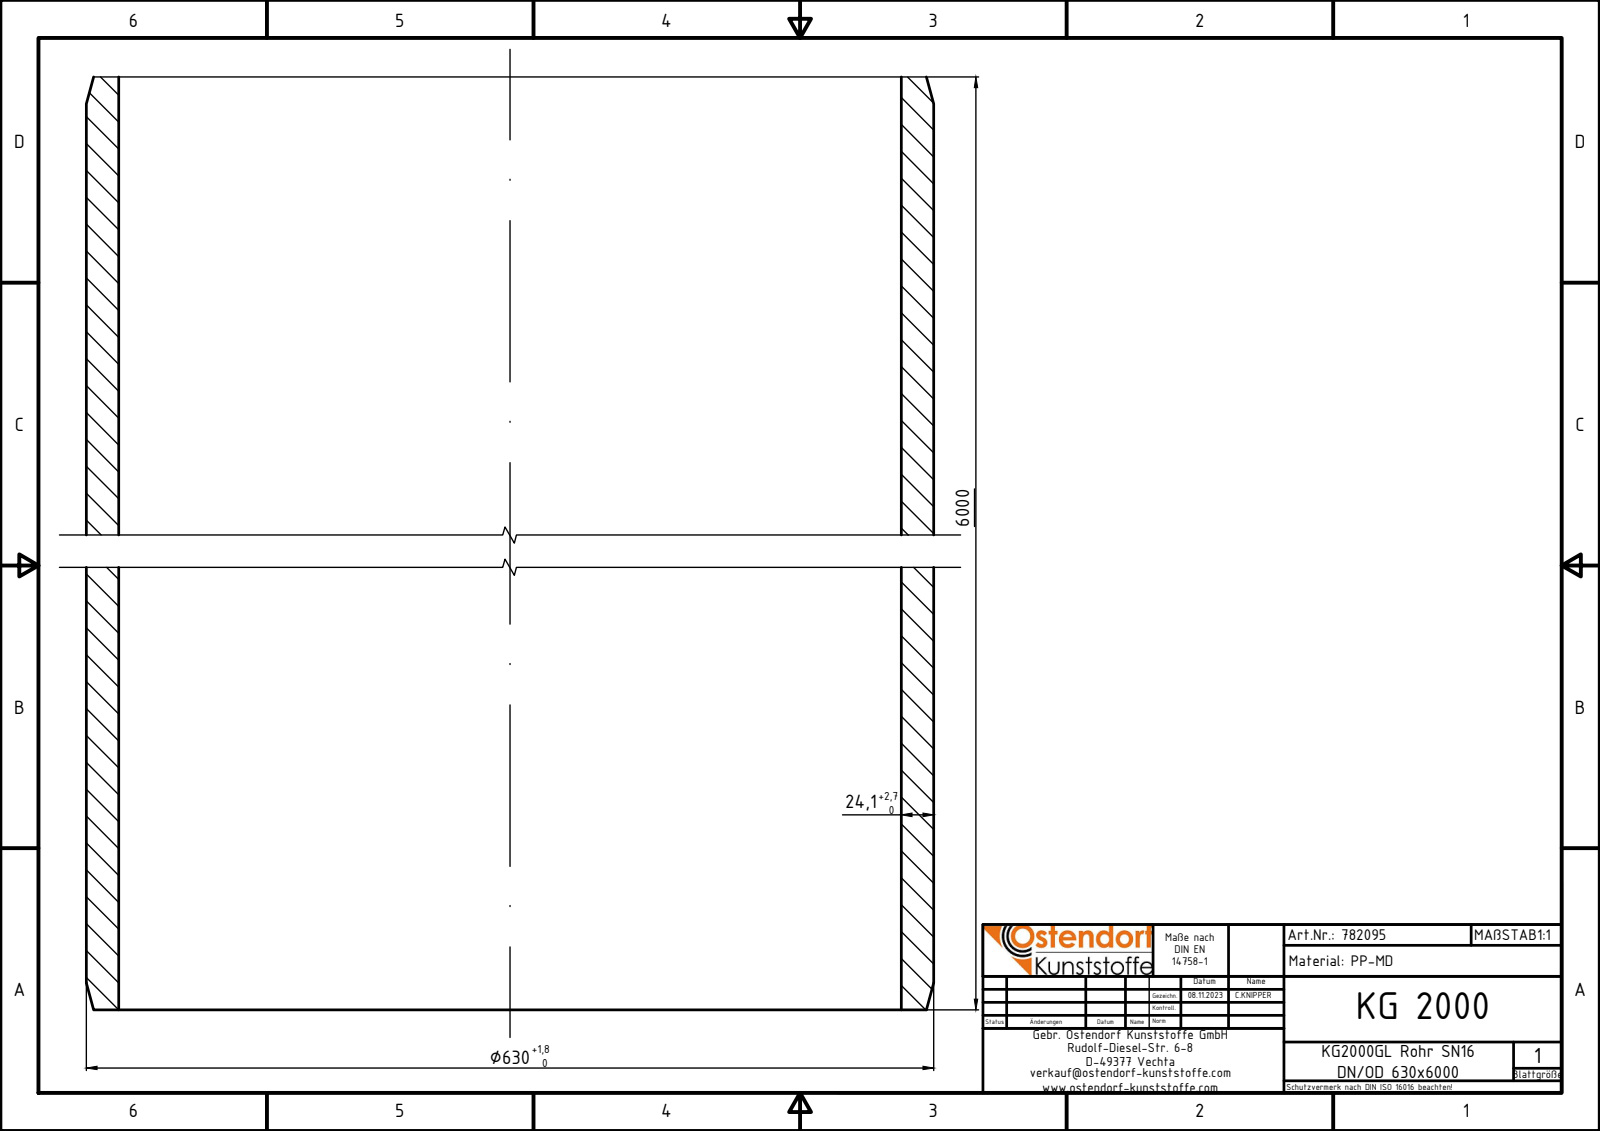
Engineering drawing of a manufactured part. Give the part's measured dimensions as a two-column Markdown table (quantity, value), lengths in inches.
| quantity | value |
| --- | --- |
| part name | 782095z |
| STEP written by | Autodesk Inventor 2024 (AUTOMOTIVE_DESIGN) |
| units | inches |
| bodies | 1 solid, 6 faces (2 planar, 2 cylindrical, 2 other) |
| overall size | 236.22 × 24.803 × 24.803 |
| volume | 16 780 in³ |
| surface area | 35 510 in² |
| round holes (diameter × count) | 22.906 × 1 |
| round bosses / shafts (diameter × count) | 24.803 × 1 |
| main face-to-face distances | 236.22 |
